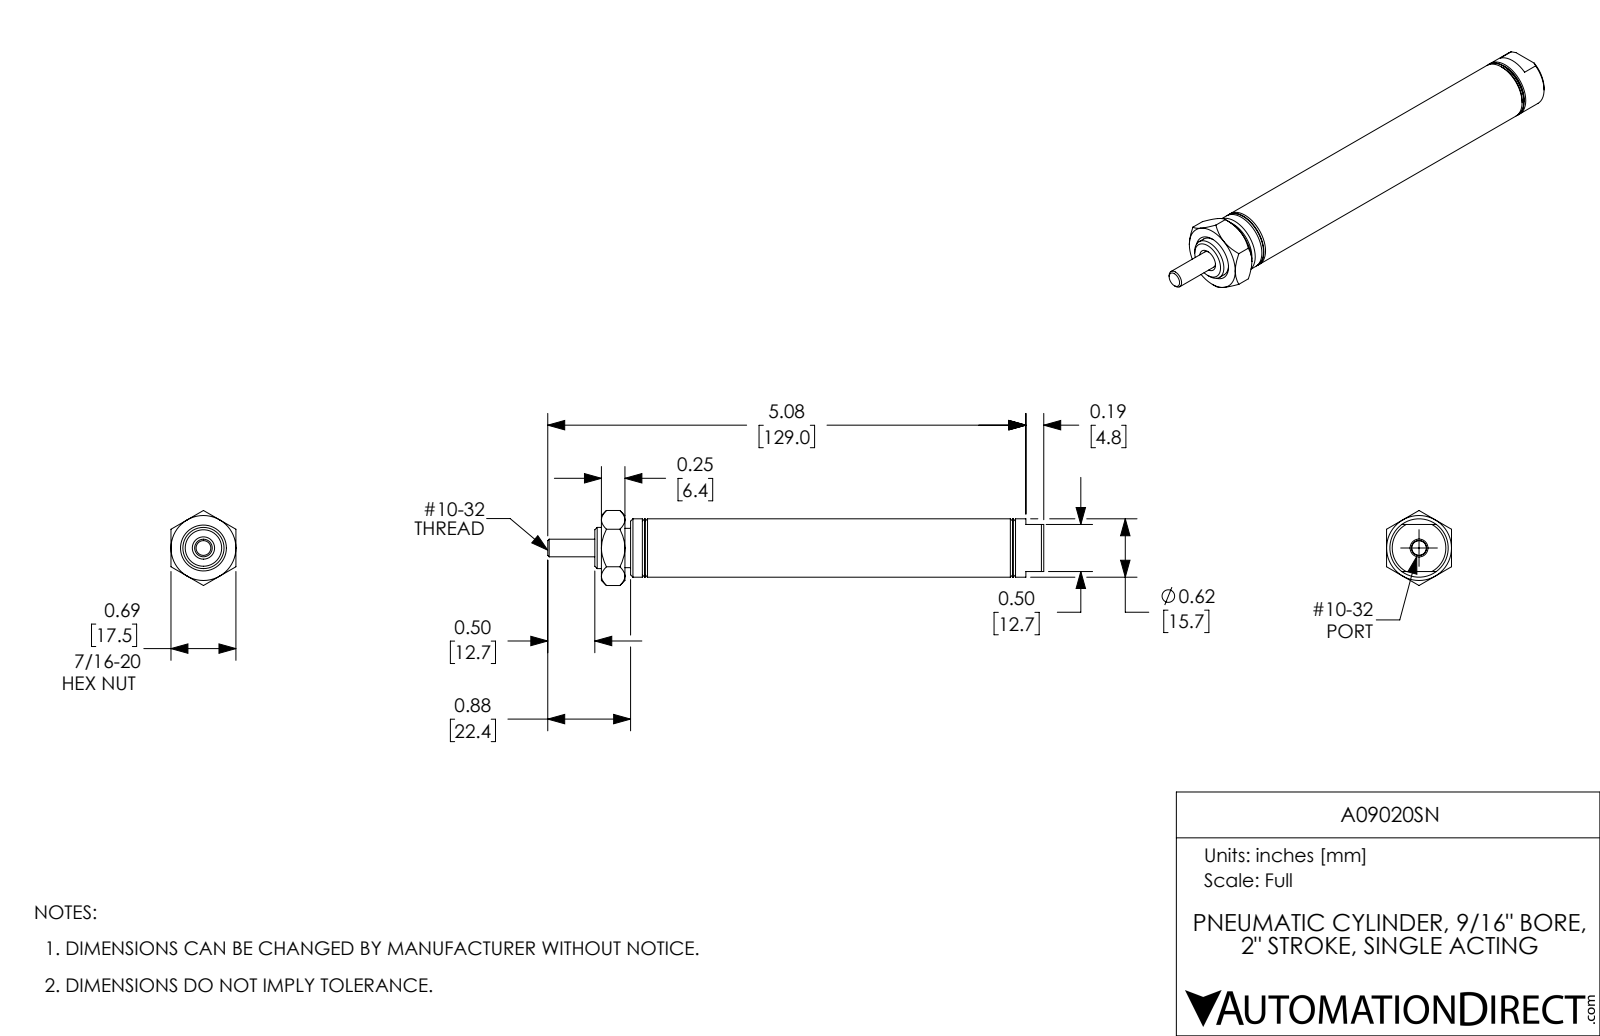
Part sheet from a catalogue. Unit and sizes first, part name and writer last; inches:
Units: inches
Overall size (bounding box): 5.27 × 0.797 × 0.69
Round holes (diameter × count): ⌀0.156 ×1, ⌀0.159 ×1, ⌀0.187 ×1, ⌀0.19 ×1, ⌀0.437 ×1, ⌀0.563 ×1
Round bosses / shafts (diameter × count): ⌀0.62 ×1, ⌀0.417 ×1
Main face-to-face distances: 0.945, 3.445, 0.5, 0.69, 1.255, 3.255, 2.5, 1.005, 4.45, 3.505
Volume: 0.987 in³ · Surface area: 20.92 in²
Bodies: 3 solids, 95 faces (27 planar, 30 cylindrical, 38 other)
Part name (STEP PRODUCT): A09020SN; A09020SN_Mounting Nut_D-154; A09020SN-Rod; A09020SN-MainBody
STEP written by: SolidWorks 2017 (AUTOMOTIVE_DESIGN)
